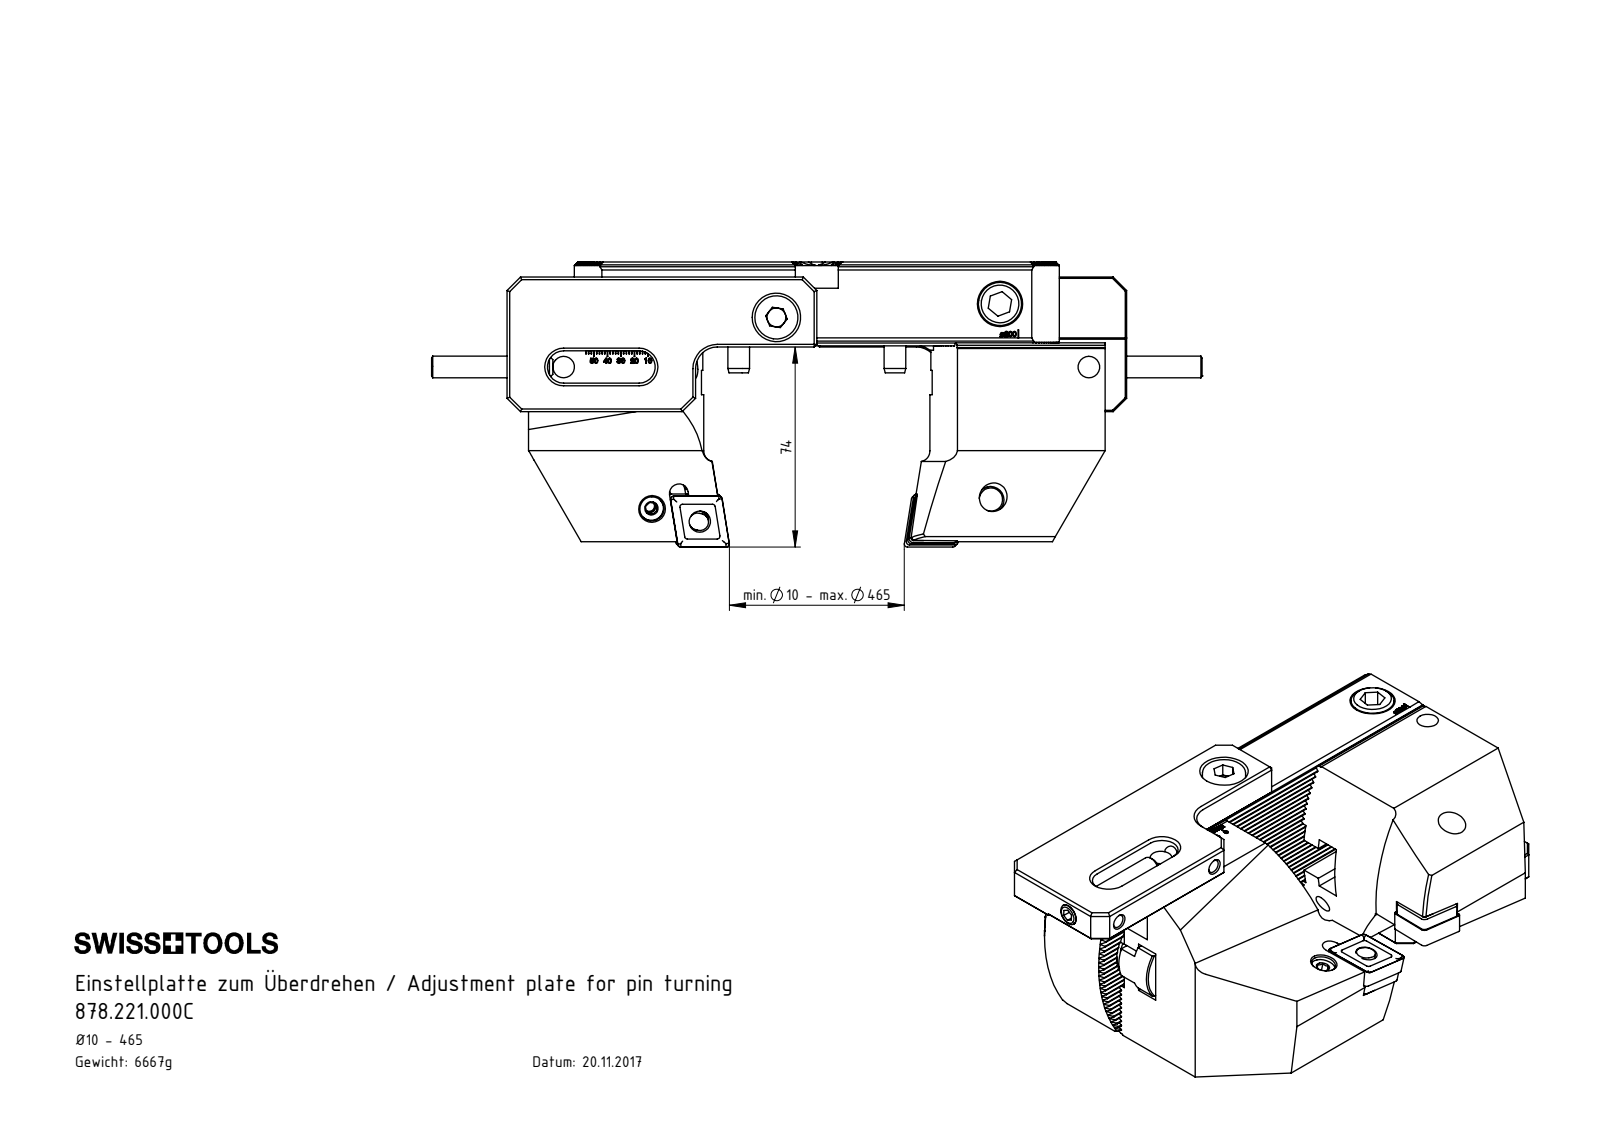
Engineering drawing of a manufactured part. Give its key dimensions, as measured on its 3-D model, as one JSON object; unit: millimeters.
{"part_name": "ISO 4026 - M8 x 45; 878.221.000C; ISO 8734 - 6 x 14; VK1-ER7.002.012_C (+1 more)", "step_written_by": "SolidWorks 2022 (AUTOMOTIVE_DESIGN)", "units": "millimeters", "bodies": {"solids": 5, "faces": 139, "planar": 74, "cylindrical": 30, "other": 35}, "overall_size": [126.3, 50, 22], "volume_mm3": 50069, "surface_area_mm2": 17562, "round_holes": [[5, 2], [6, 2], [6.8, 1], [11, 1], [18, 1]], "round_bosses_or_shafts": [[16, 1], [10, 1], [8, 1]], "partial_cylinders_radius": [[6, 2], [8, 1]], "face_to_face_distances": [12, 0.5, 11.5, 50, 6, 26, 24, 5.5, 27.4, 39.4], "hole_center_spacings": [7.9, 18.55, 19.61, 50]}
